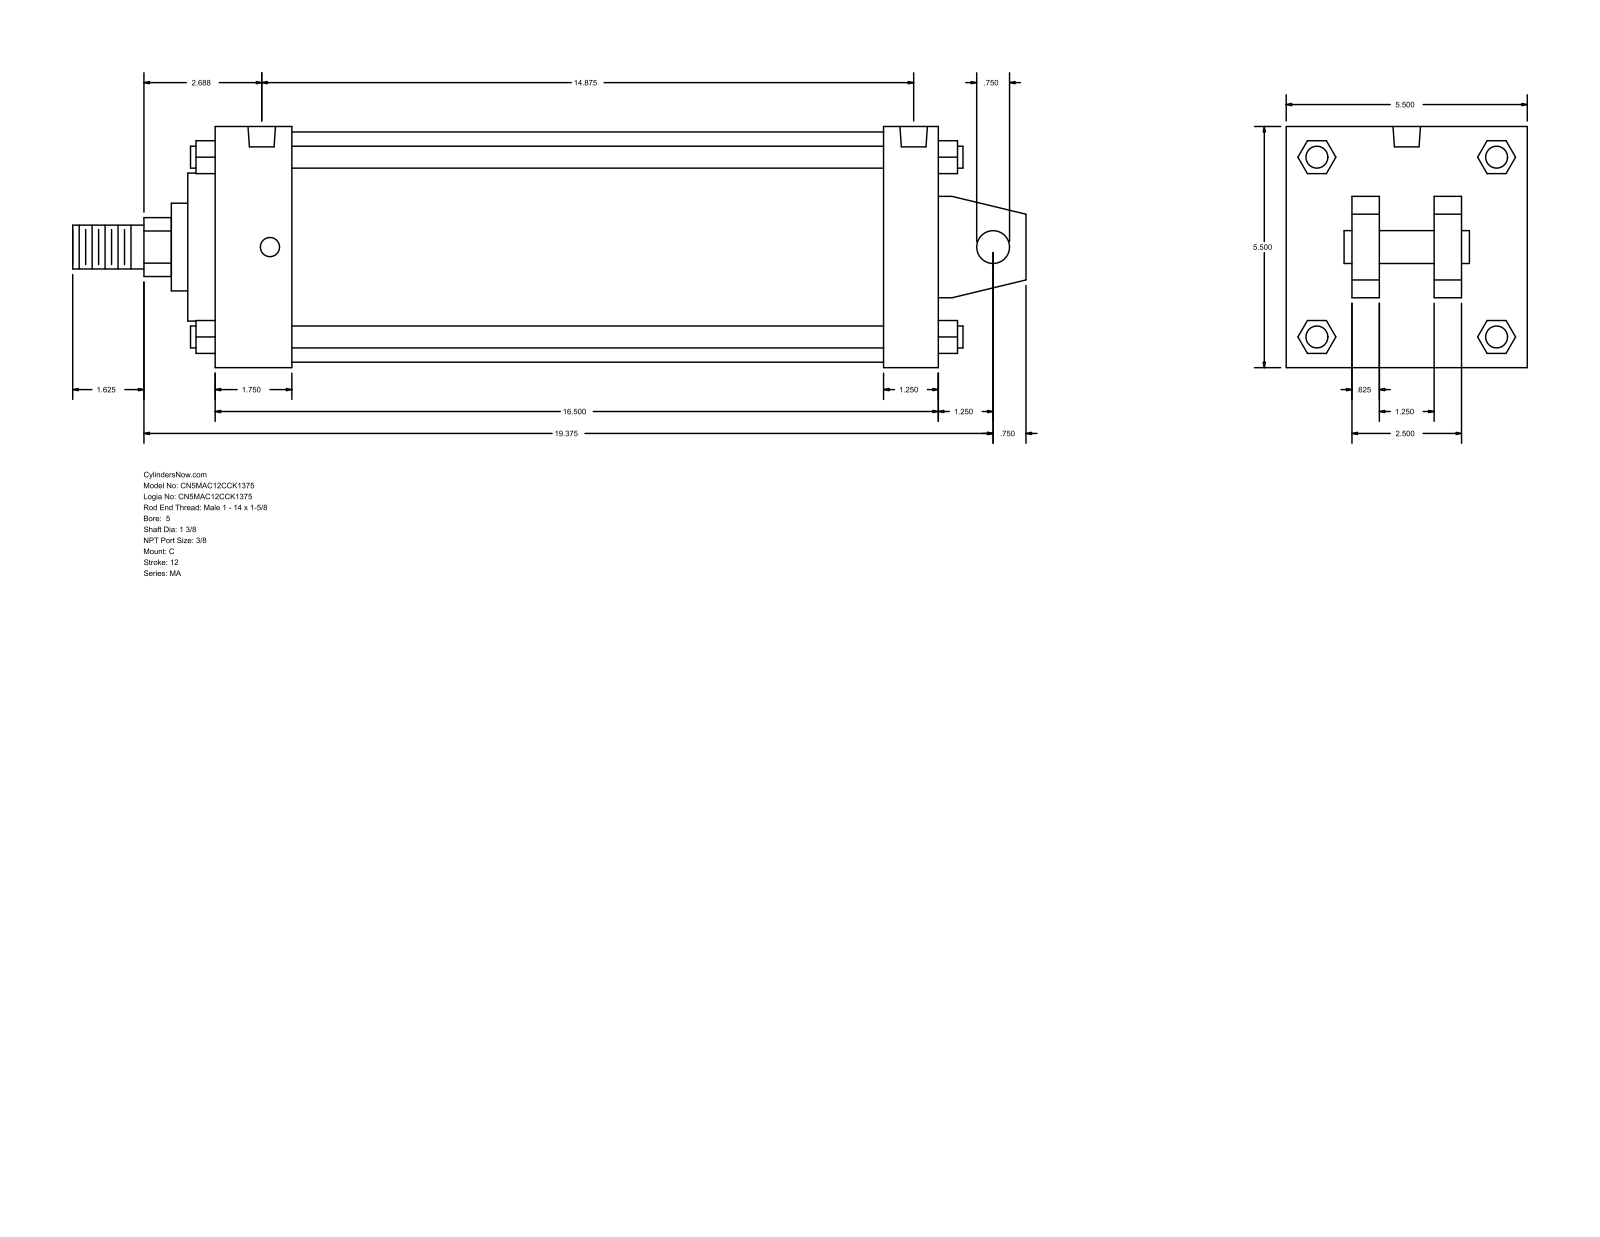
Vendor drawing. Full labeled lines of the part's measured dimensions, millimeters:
Part name (STEP PRODUCT): MA_C__0500_1.375
STEP written by: GSSL Pune (CONFIG_CONTROL_DESIGN)
Units: millimetres
Bodies: 0 solids, 141 faces (109 planar, 32 cylindrical, 0 other)
Overall size (bounding box): 552.45 × 139.7 × 139.7
Round holes (diameter × count): ⌀11.11 ×4, ⌀15.93 ×2
Round bosses / shafts (diameter × count): ⌀12.7 ×4, ⌀133.35 ×1, ⌀85.72 ×1, ⌀50.8 ×1, ⌀34.92 ×1, ⌀25.4 ×1, ⌀19.05 ×1
Partial cylindrical surfaces — rounded edges, fillets, slot ends (radius × count): R17.06 ×1
Main face-to-face distances: 139.7, 419.11, 15.87, 31.76, 387.35, 44.45, 342.9, 374.66, 53.97, 38.1
Hole centre spacings: 4.77, 368.29, 373.06, 377.83
